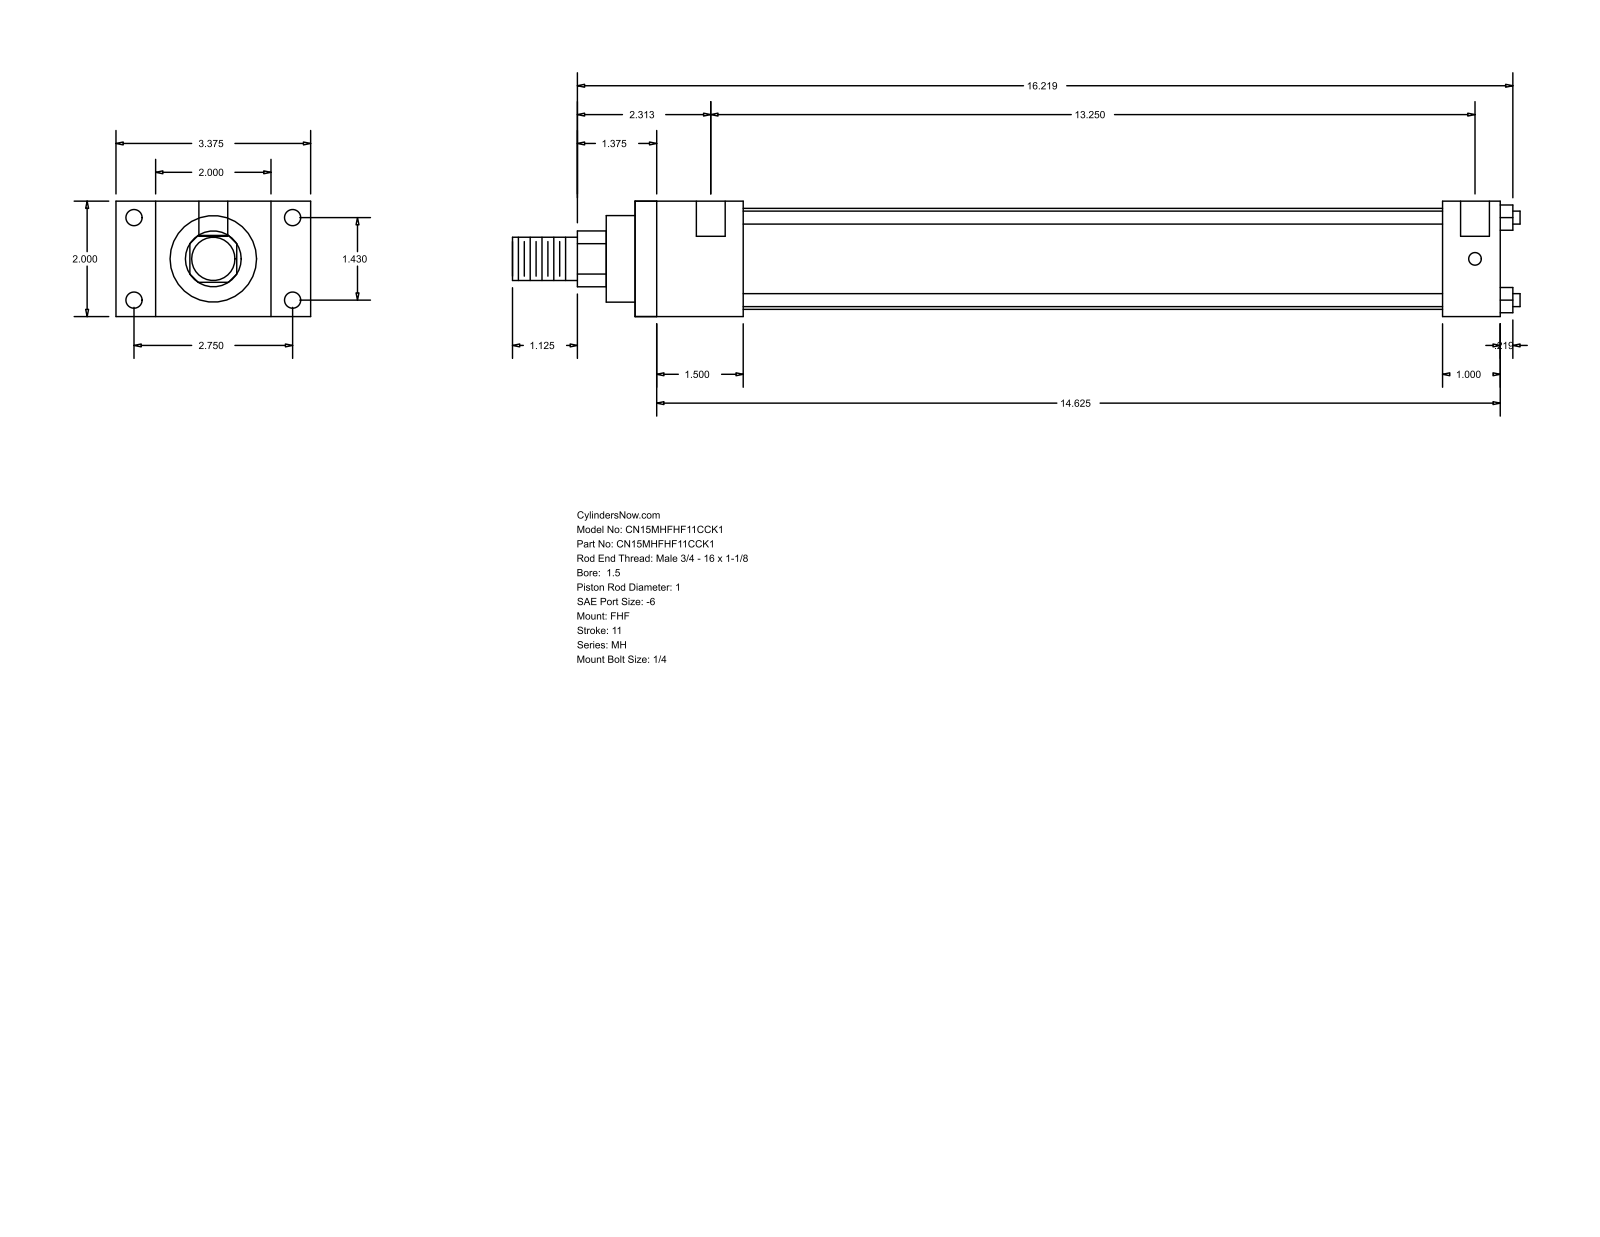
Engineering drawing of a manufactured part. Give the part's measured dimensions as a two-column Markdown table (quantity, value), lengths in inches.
| quantity | value |
| --- | --- |
| part name | MH_FHF__0150_1 |
| STEP written by | GSSL Pune (CONFIG_CONTROL_DESIGN) |
| units | inches |
| bodies | 0 solids, 88 faces (60 planar, 28 cylindrical, 0 other) |
| overall size | 17.469 × 3.375 × 2 |
| round holes (diameter × count) | 0.219 × 4, 0.281 × 4, 0.5 × 2 |
| round bosses / shafts (diameter × count) | 0.225 × 4, 1.75 × 1, 1.5 × 1, 1 × 1, 0.75 × 1 |
| partial cylindrical surfaces (radius × count) | 0.484 × 1 |
| main face-to-face distances | 2, 0.687, 2.687, 1.875, 3.375, 15, 13.125, 1, 14, 12.125 |
| hole center spacings | 1.43, 2.75, 3.099, 13.375, 0.125, 13.25 |
